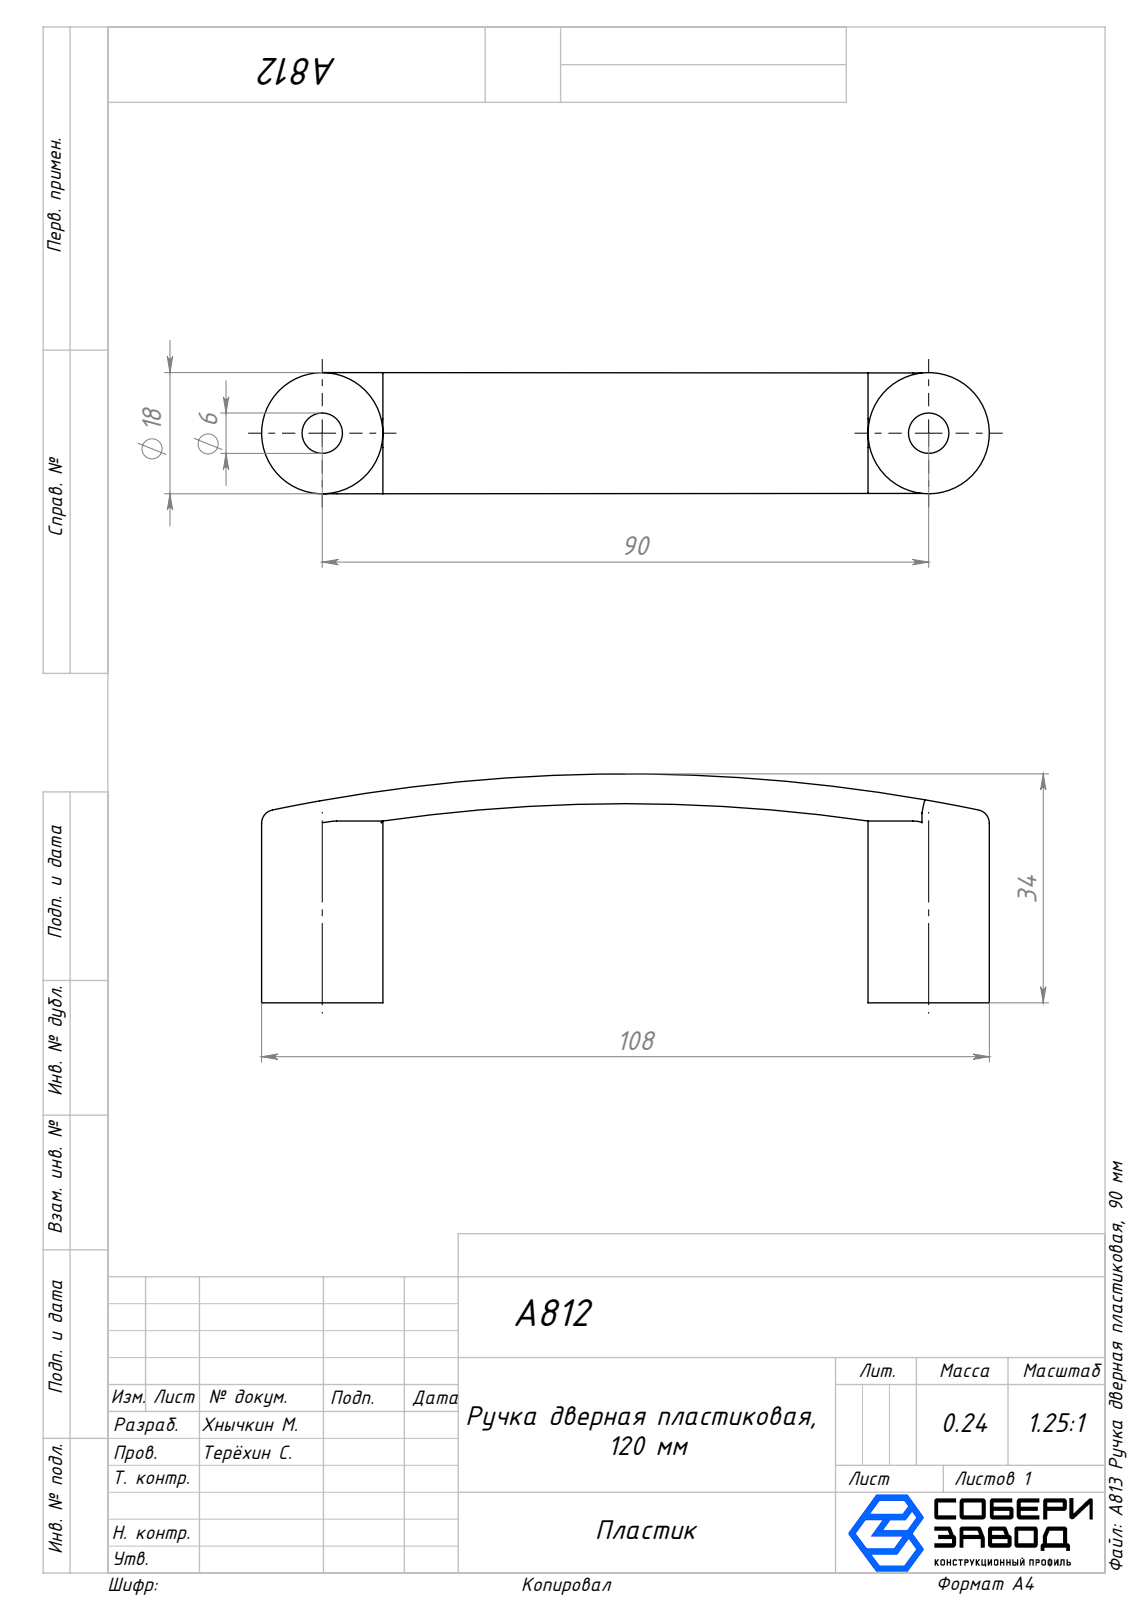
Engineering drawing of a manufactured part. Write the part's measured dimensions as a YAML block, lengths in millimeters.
part_name: "A813 Ручка дверная пластиковая, 90 мм"
step_written_by: "SolidWorks 2025 (AUTOMOTIVE_DESIGN)"
units: millimeters
bodies: {solids: 1, faces: 32, planar: 10, cylindrical: 10, other: 12}
overall_size: [108, 34, 18]
volume: 19587
surface_area: 8516
round_holes:
  - {diameter: 6, count: 2}
round_bosses_or_shafts:
  - {diameter: 18, count: 2}
partial_cylinders:
  - {radius: 252.93, count: 1}
  - {radius: 258.64, count: 1}
face_to_face_distances: [27]
hole_center_spacings: [90]
